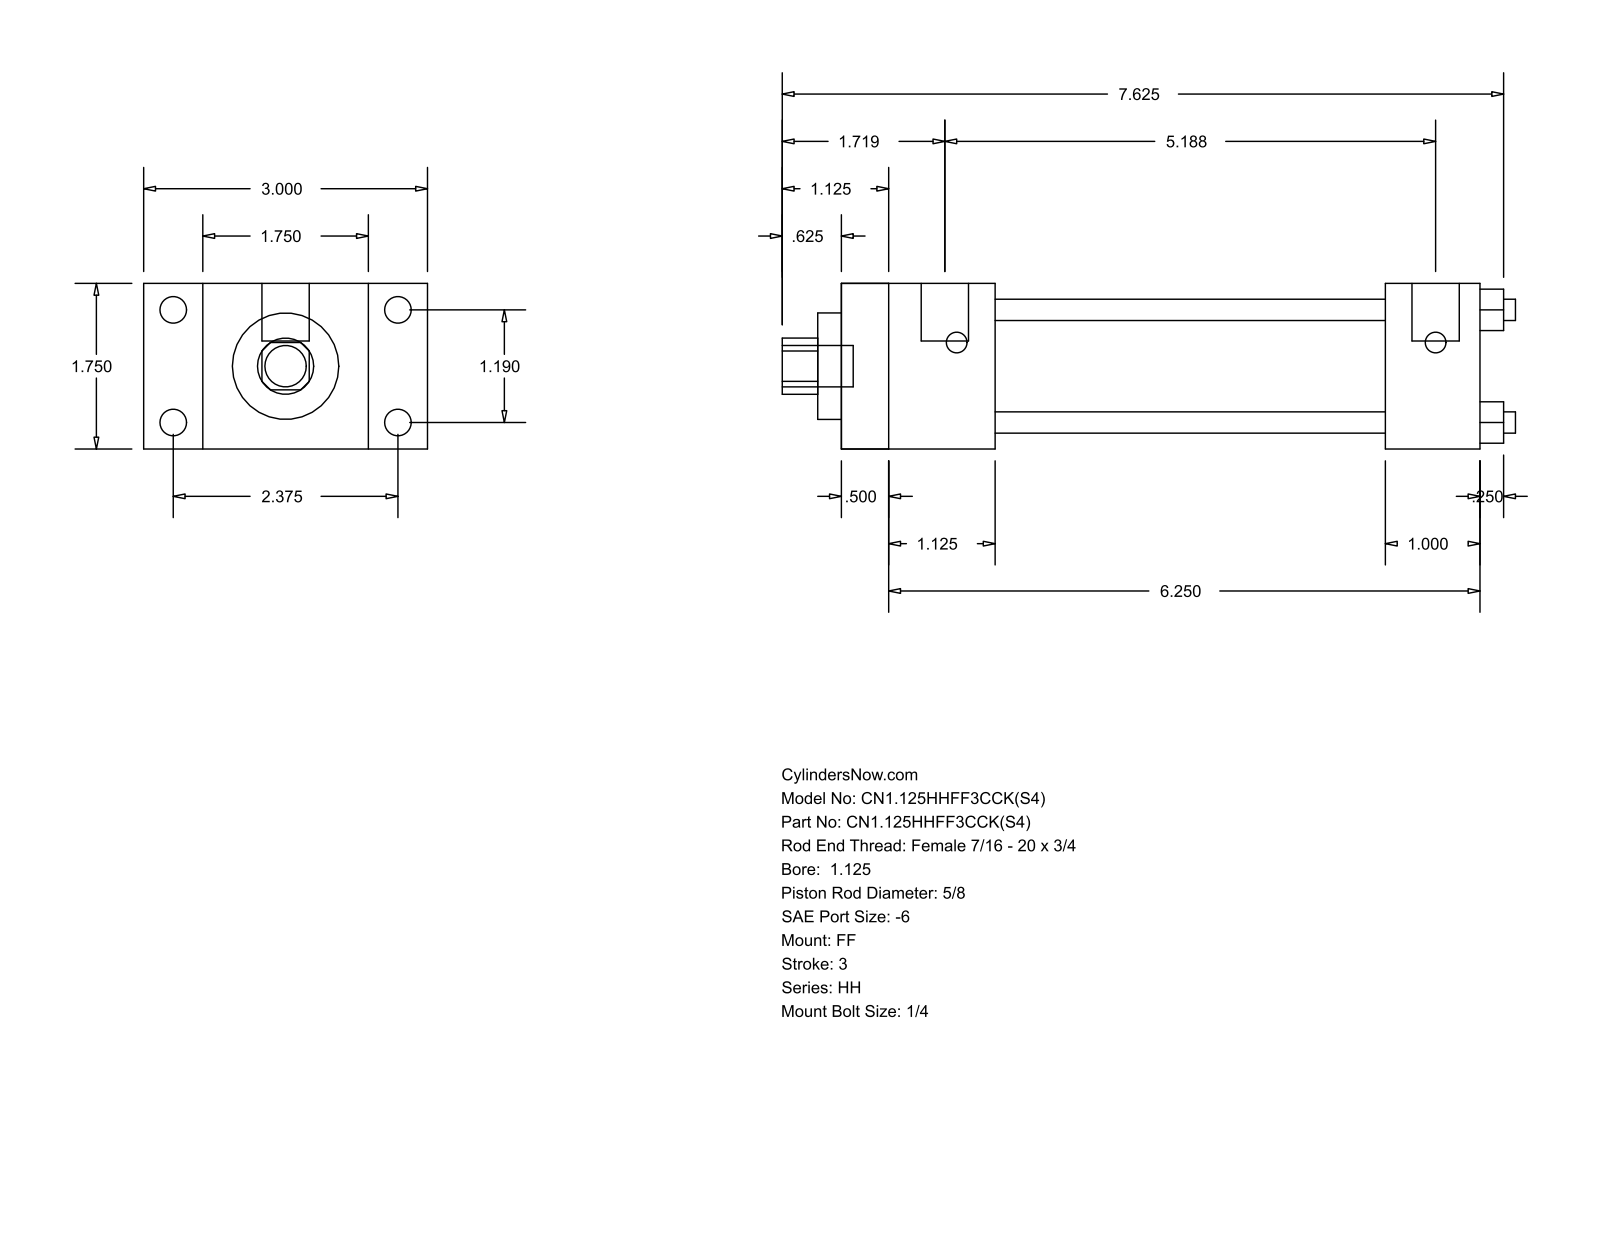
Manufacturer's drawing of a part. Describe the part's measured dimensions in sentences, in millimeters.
The part is named "HH_FF__0112_0.625". Its 3-D file was written by "GSSL Pune (CONFIG_CONTROL_DESIGN)". It is 0 solids with 92 faces: 64 planar, 28 cylindrical and 0 other. Overall it measures 196.85 by 76.2 by 44.45 millimeters. Round holes: 4 of diameter 5.71, 1 of diameter 15.88, 1 of diameter 28.57, 1 of diameter 34.92. Round bosses or shafts: 4 of diameter 7.14, 4 of diameter 5.56, 2 of diameter 12.7, 1 of diameter 11.11. Partial cylindrical surfaces (rounded edges, fillets, slot ends): 1 of radius 7.54. The main face-to-face distances are 44.46, 171.44, 12.69, 158.75, 15.87, 60.33, 28.58, 41.27, 146.05, 133.36. The hole center spacings are 21.37, 30.22, 42.74.
